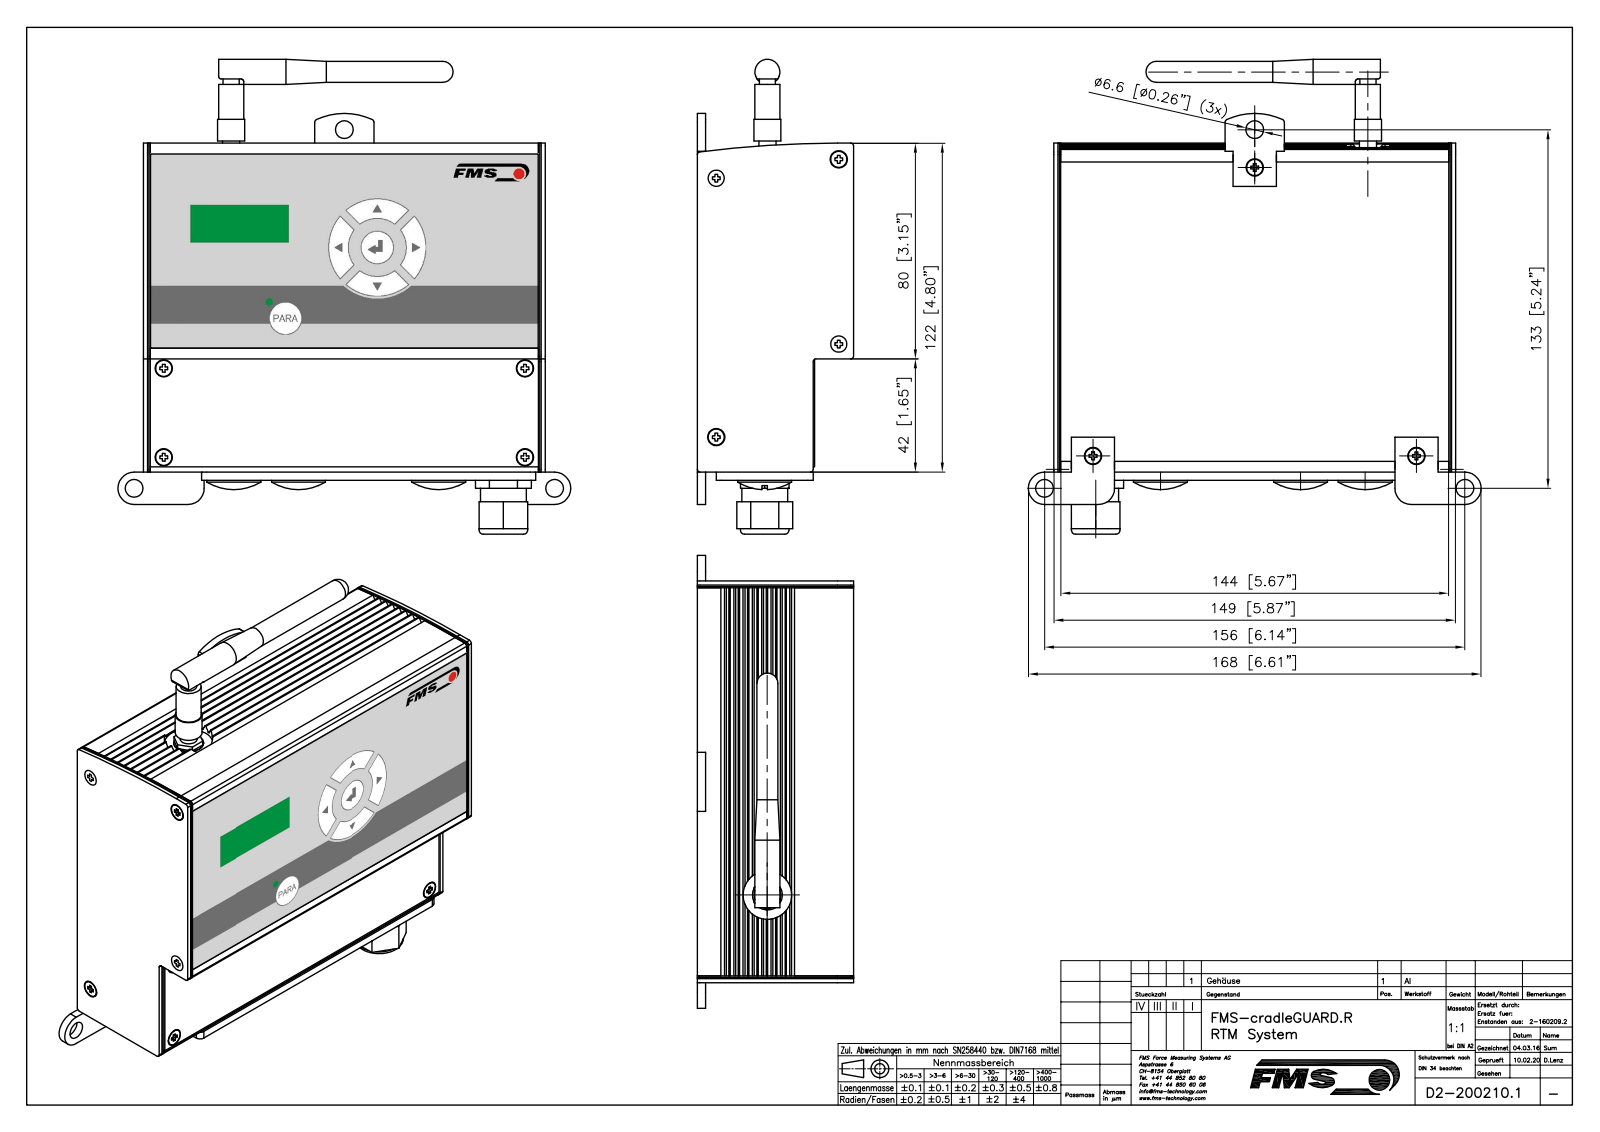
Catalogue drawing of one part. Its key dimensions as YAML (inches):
part_name: "T2002101_STP; T1002162; T1002151; T1002152 (+8 more)"
step_written_by: "Mechanical Desktop 2009 (CONFIG_CONTROL_DESIGN)"
units: inches
bodies: {solids: 40, faces: 1042, planar: 564, cylindrical: 319, other: 159}
overall_size: [7.655, 6.933, 2.283]
volume: 14.77
surface_area: 299
round_holes:
  - {diameter: 0.126, count: 17}
  - {diameter: 0.102, count: 16}
  - {diameter: 0.094, count: 4}
  - {diameter: 0.472, count: 4}
  - {diameter: 0.578, count: 4}
  - {diameter: 0.26, count: 3}
  - {diameter: 0.25, count: 1}
  - {diameter: 0.256, count: 1}
  - {diameter: 0.315, count: 1}
  - {diameter: 0.394, count: 1}
  - {diameter: 0.433, count: 1}
  - {diameter: 0.531, count: 1}
round_bosses_or_shafts:
  - {diameter: 0.236, count: 18}
  - {diameter: 0.118, count: 17}
  - {diameter: 0.63, count: 4}
  - {diameter: 0.787, count: 3}
  - {diameter: 0.366, count: 2}
  - {diameter: 0.709, count: 1}
  - {diameter: 0.669, count: 1}
  - {diameter: 0.61, count: 1}
partial_cylinders:
  - {radius: 0.079, count: 12}
  - {radius: 0.039, count: 10}
  - {radius: 0.157, count: 4}
  - {radius: 0.197, count: 4}
  - {radius: 0.236, count: 4}
  - {radius: 0.315, count: 4}
  - {radius: 0.984, count: 1}
  - {radius: 15.748, count: 1}
face_to_face_distances: [0.02, 0.118, 0.098, 0.079, 5.709, 0.039, 0.059, 5.728, 5.689, 5.768]
hole_center_spacings: [0.604, 0.941, 0.945, 2.853, 3.783, 0.276, 0.626, 0.852]
